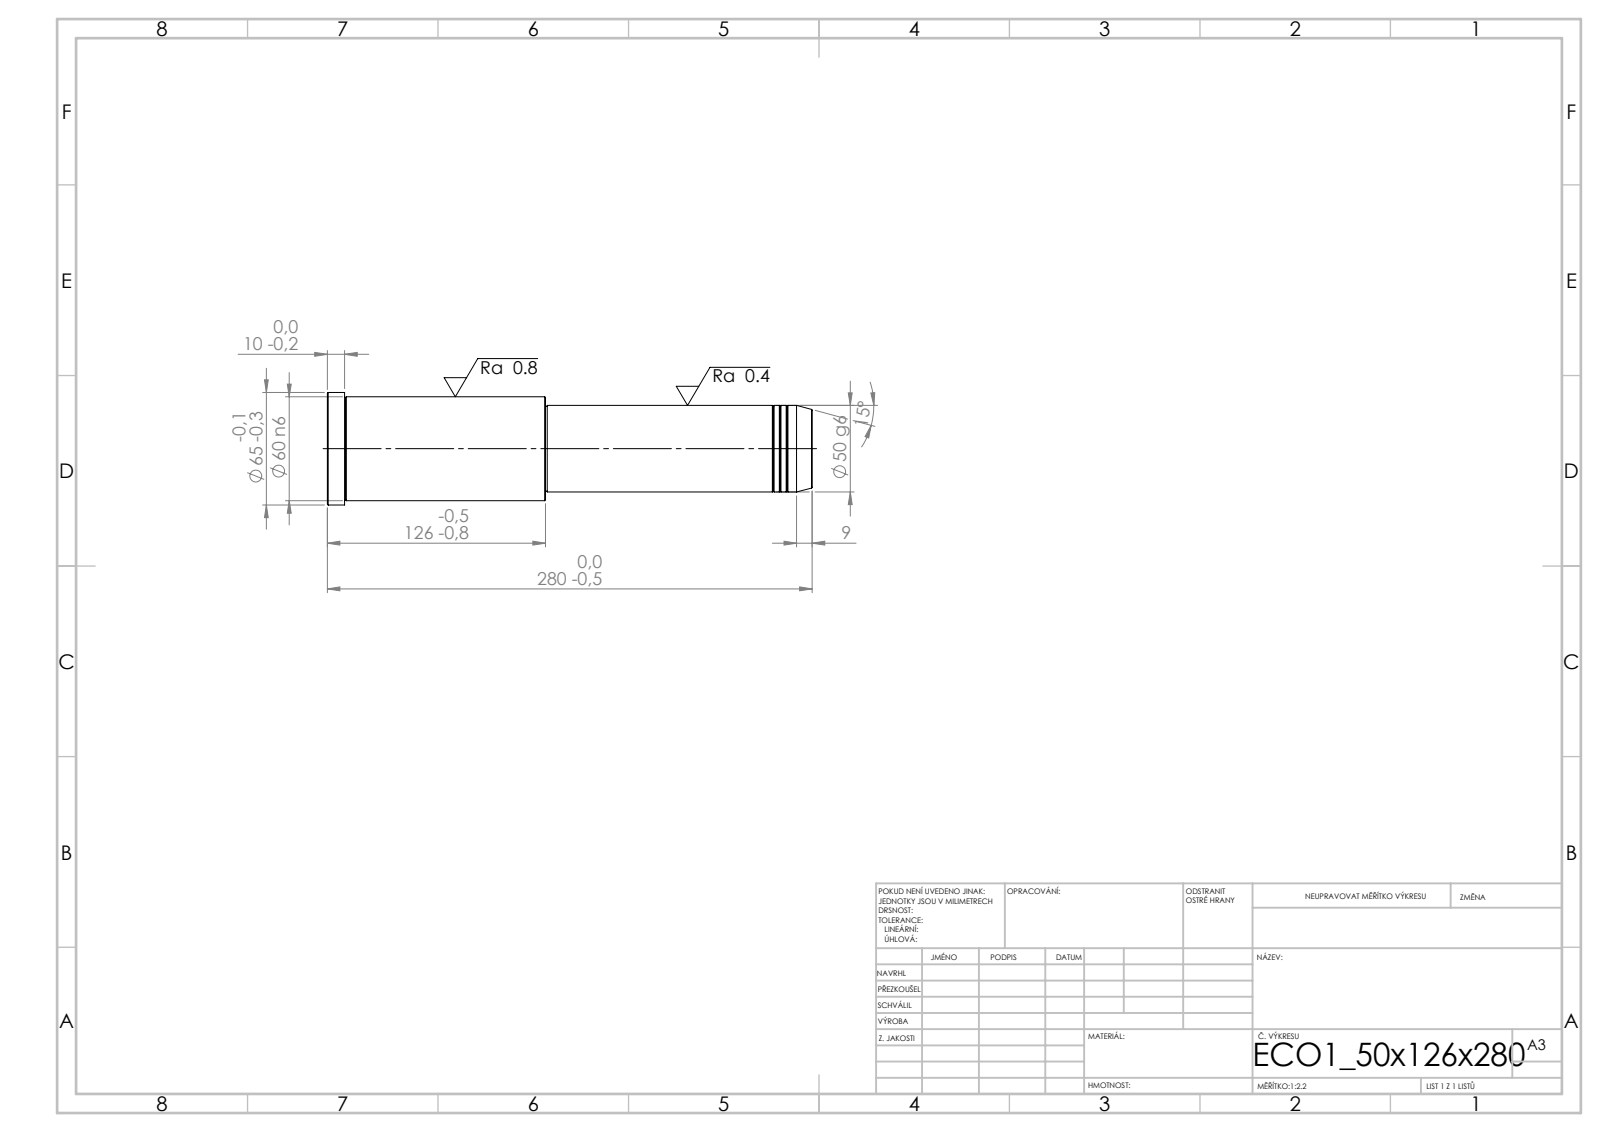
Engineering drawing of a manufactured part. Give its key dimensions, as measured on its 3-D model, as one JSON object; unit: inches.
{"step_written_by": "SolidWorks 2019 (CONFIG_CONTROL_DESIGN)", "units": "inches", "bodies": {"solids": 1, "faces": 43, "planar": 5, "cylindrical": 14, "other": 24}, "overall_size": [11.024, 2.559, 2.559], "volume_in3": 40.37, "surface_area_in2": 84.84, "round_bosses_or_shafts": [[2.559, 1], [2.362, 1], [1.969, 1], [1.929, 1]], "face_to_face_distances": [11.024, 6.063, 4.961, 10.63, 4.567, 0.394, 6.024, 0.039, 4.606, 5]}
